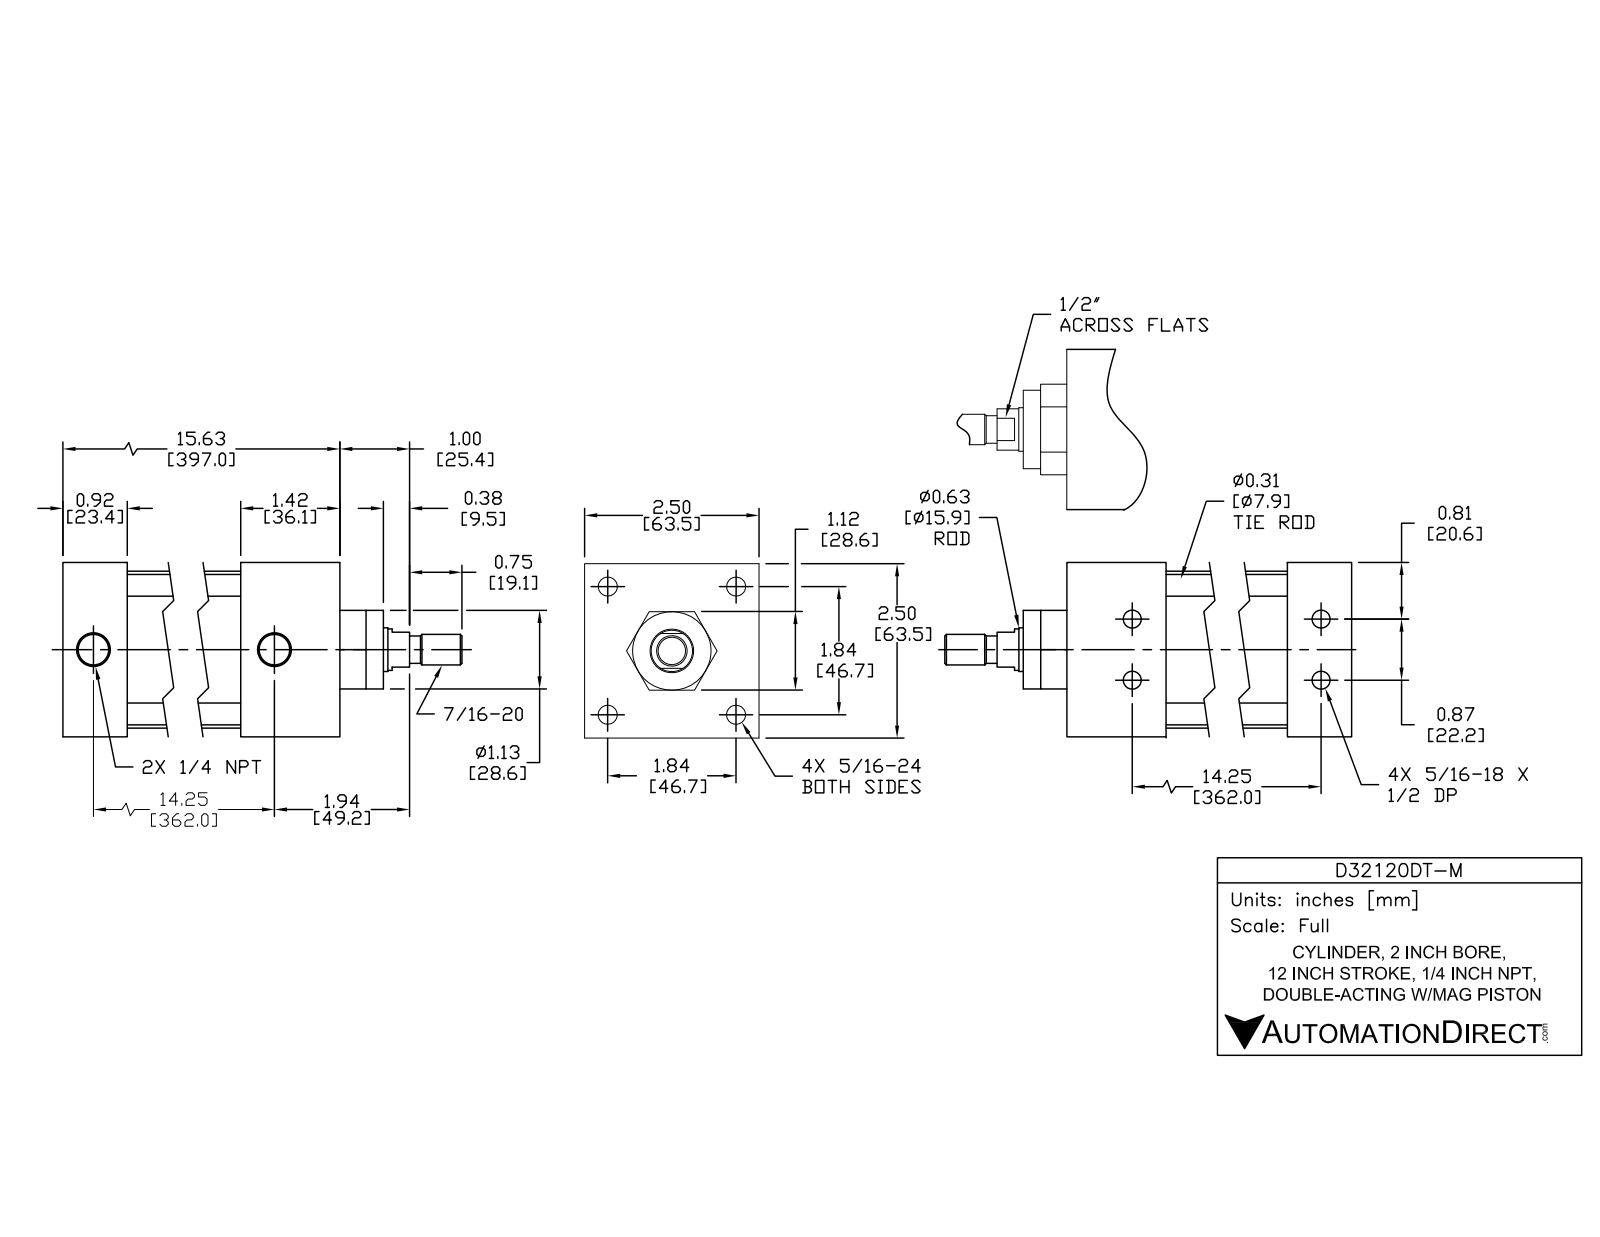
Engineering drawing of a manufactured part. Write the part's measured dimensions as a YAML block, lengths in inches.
part_name: "D32120DT-M; D32120DT-M BODY; D32120DT-M PISTON"
step_written_by: "SolidWorks 2015 (AUTOMOTIVE_DESIGN)"
units: inches
bodies: {solids: 12, faces: 298, planar: 94, cylindrical: 114, other: 90}
overall_size: [17.371, 2.5, 2.5]
volume: 36.5
surface_area: 349.7
round_holes:
  - {diameter: 0.252, count: 4}
  - {diameter: 0.267, count: 4}
  - {diameter: 0.359, count: 4}
  - {diameter: 0.5, count: 4}
  - {diameter: 0.297, count: 2}
  - {diameter: 0.477, count: 2}
  - {diameter: 0.625, count: 1}
  - {diameter: 0.628, count: 1}
  - {diameter: 2, count: 1}
round_bosses_or_shafts:
  - {diameter: 0.484, count: 4}
  - {diameter: 0.313, count: 4}
  - {diameter: 0.282, count: 4}
  - {diameter: 2.25, count: 1}
  - {diameter: 1.997, count: 1}
  - {diameter: 1.12, count: 1}
  - {diameter: 0.622, count: 1}
  - {diameter: 0.59, count: 1}
partial_cylinders:
  - {radius: 0.25, count: 4}
face_to_face_distances: [2.5, 15.621, 1.42, 14.201, 14.701, 13.281, 0.92, 1, 14.601, 13.181]
hole_center_spacings: [1.307, 1.848, 14.252, 14.245, 0.437, 0.438, 0.875, 2.613]
